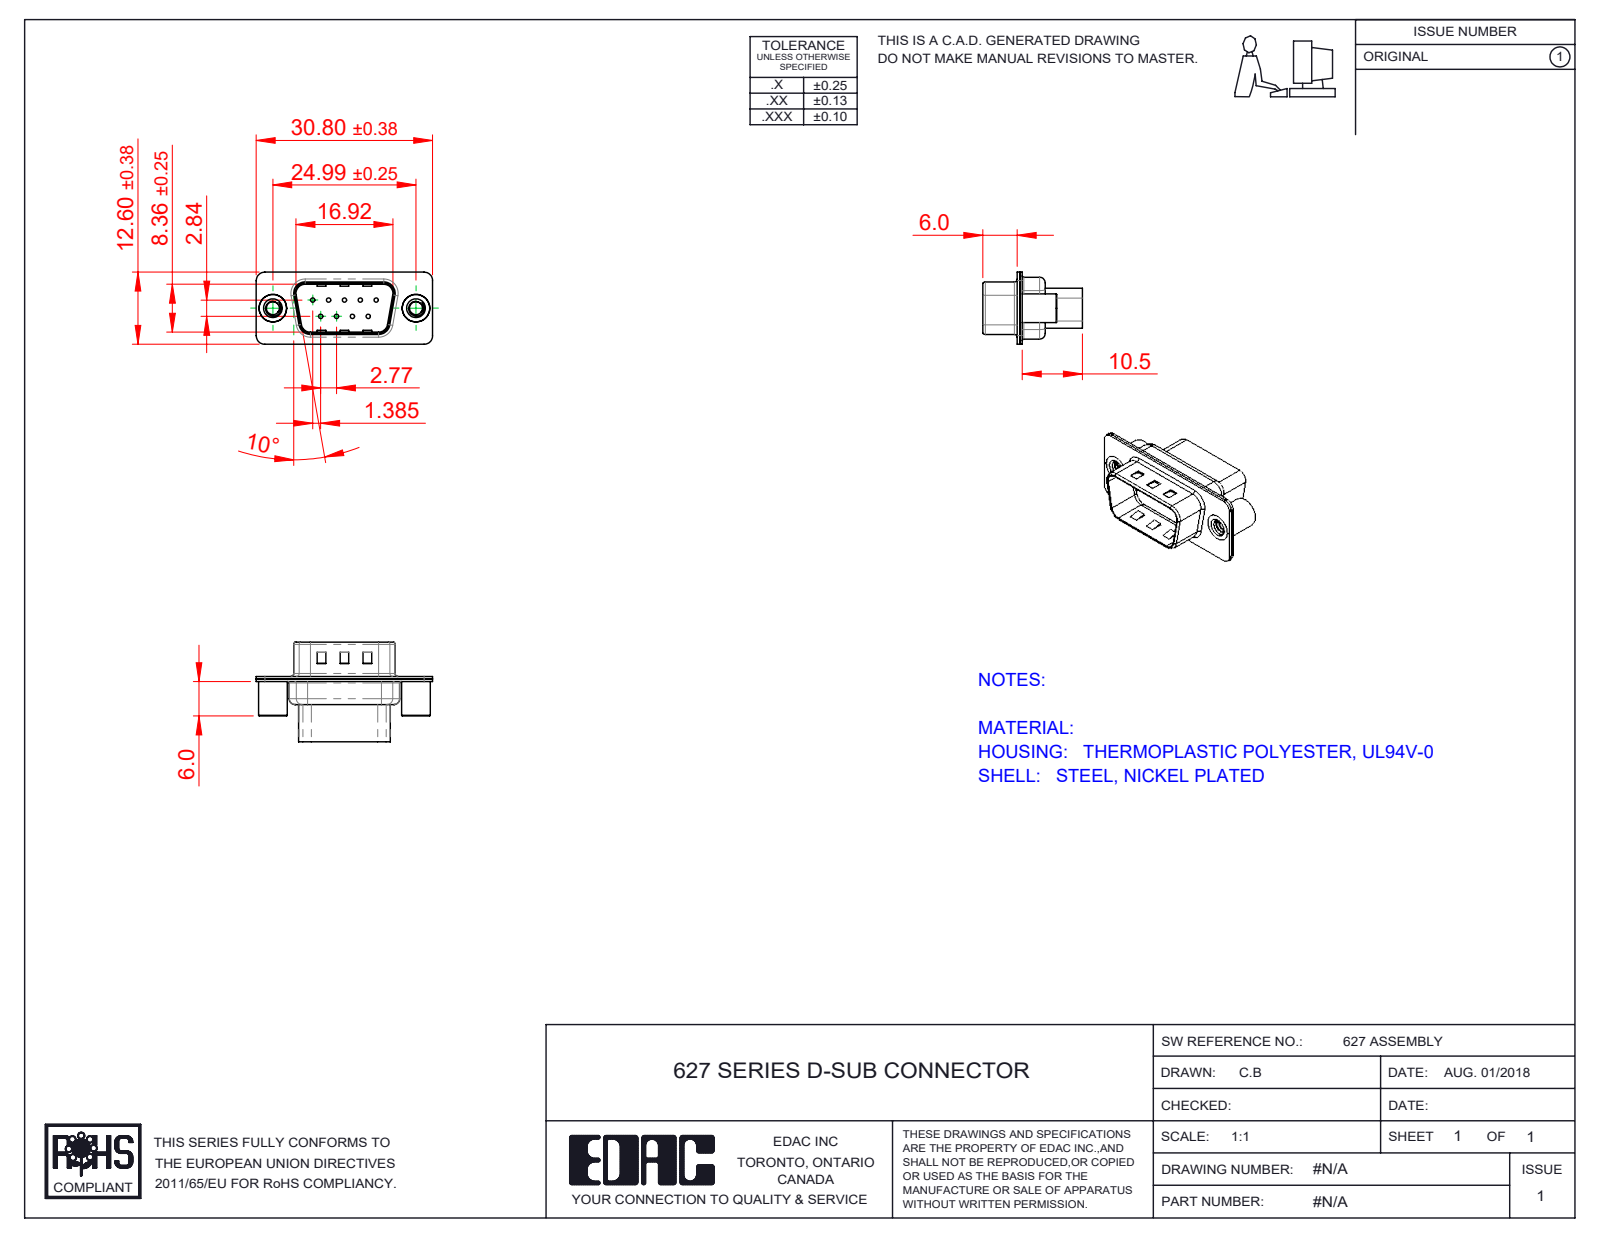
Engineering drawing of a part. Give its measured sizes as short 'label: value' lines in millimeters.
name: 627 4-40 Threaded Standoff BS; 627 Housing_09 HP; 627 Shell Front_09 Contacts; 627 Shell Rear_09 Contacts (+1 more)
written by: SolidWorks 2020 (CONFIG_CONTROL_DESIGN)
unit: mm
bodies: 5 solids, 398 faces (125 planar, 203 cylindrical, 70 other)
size: 30.8 × 17.4 × 12.6
volume: 1 763 mm³; area: 3 752 mm²
holes: 9× ⌀0.75, 9× ⌀1.6, 9× ⌀2, 2× ⌀2.26, 2× ⌀4, 2× ⌀4.8
bosses: 2× ⌀5, 2× ⌀4.9
rounds: 18× R1.5, 12× R2, 8× R0.5, 8× R1.6, 4× R0.25, 4× R0.6, 4× R0.65, 4× R0.9
face distances: 0.45, 0.4, 0.9, 0.82, 9.58, 1.4, 0.68, 7.68, 1.08, 8.08
hole spacings: 3.16, 2.77, 5.54, 5.03, 5.04, 8.31, 7.48, 7.49
